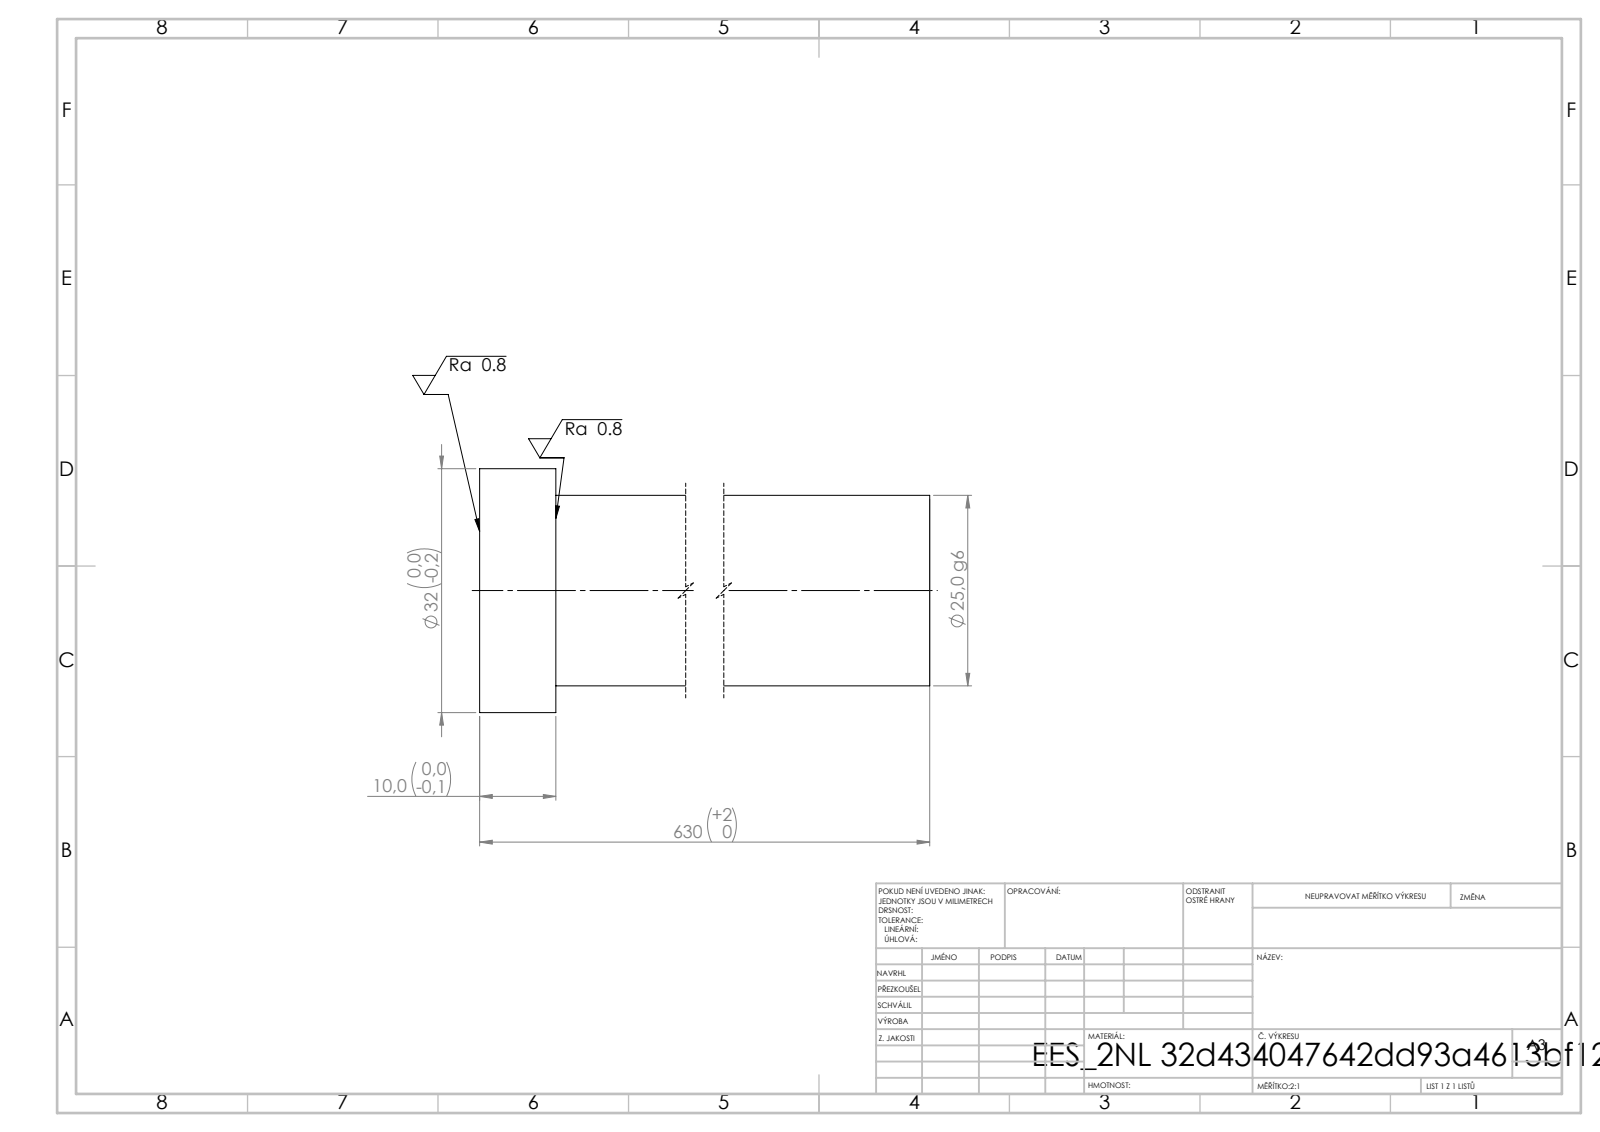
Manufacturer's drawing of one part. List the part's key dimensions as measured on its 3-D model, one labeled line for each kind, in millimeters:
STEP written by: SolidWorks 2019 (CONFIG_CONTROL_DESIGN)
Units: millimetres
Bodies: 1 solid, 7 faces (3 planar, 4 cylindrical, 0 other)
Overall size (bounding box): 630 × 32 × 32
Volume: 312 384 mm³ · Surface area: 51 308 mm²
Round bosses / shafts (diameter × count): ⌀32 ×1, ⌀25 ×1
Main face-to-face distances: 630, 10, 620
